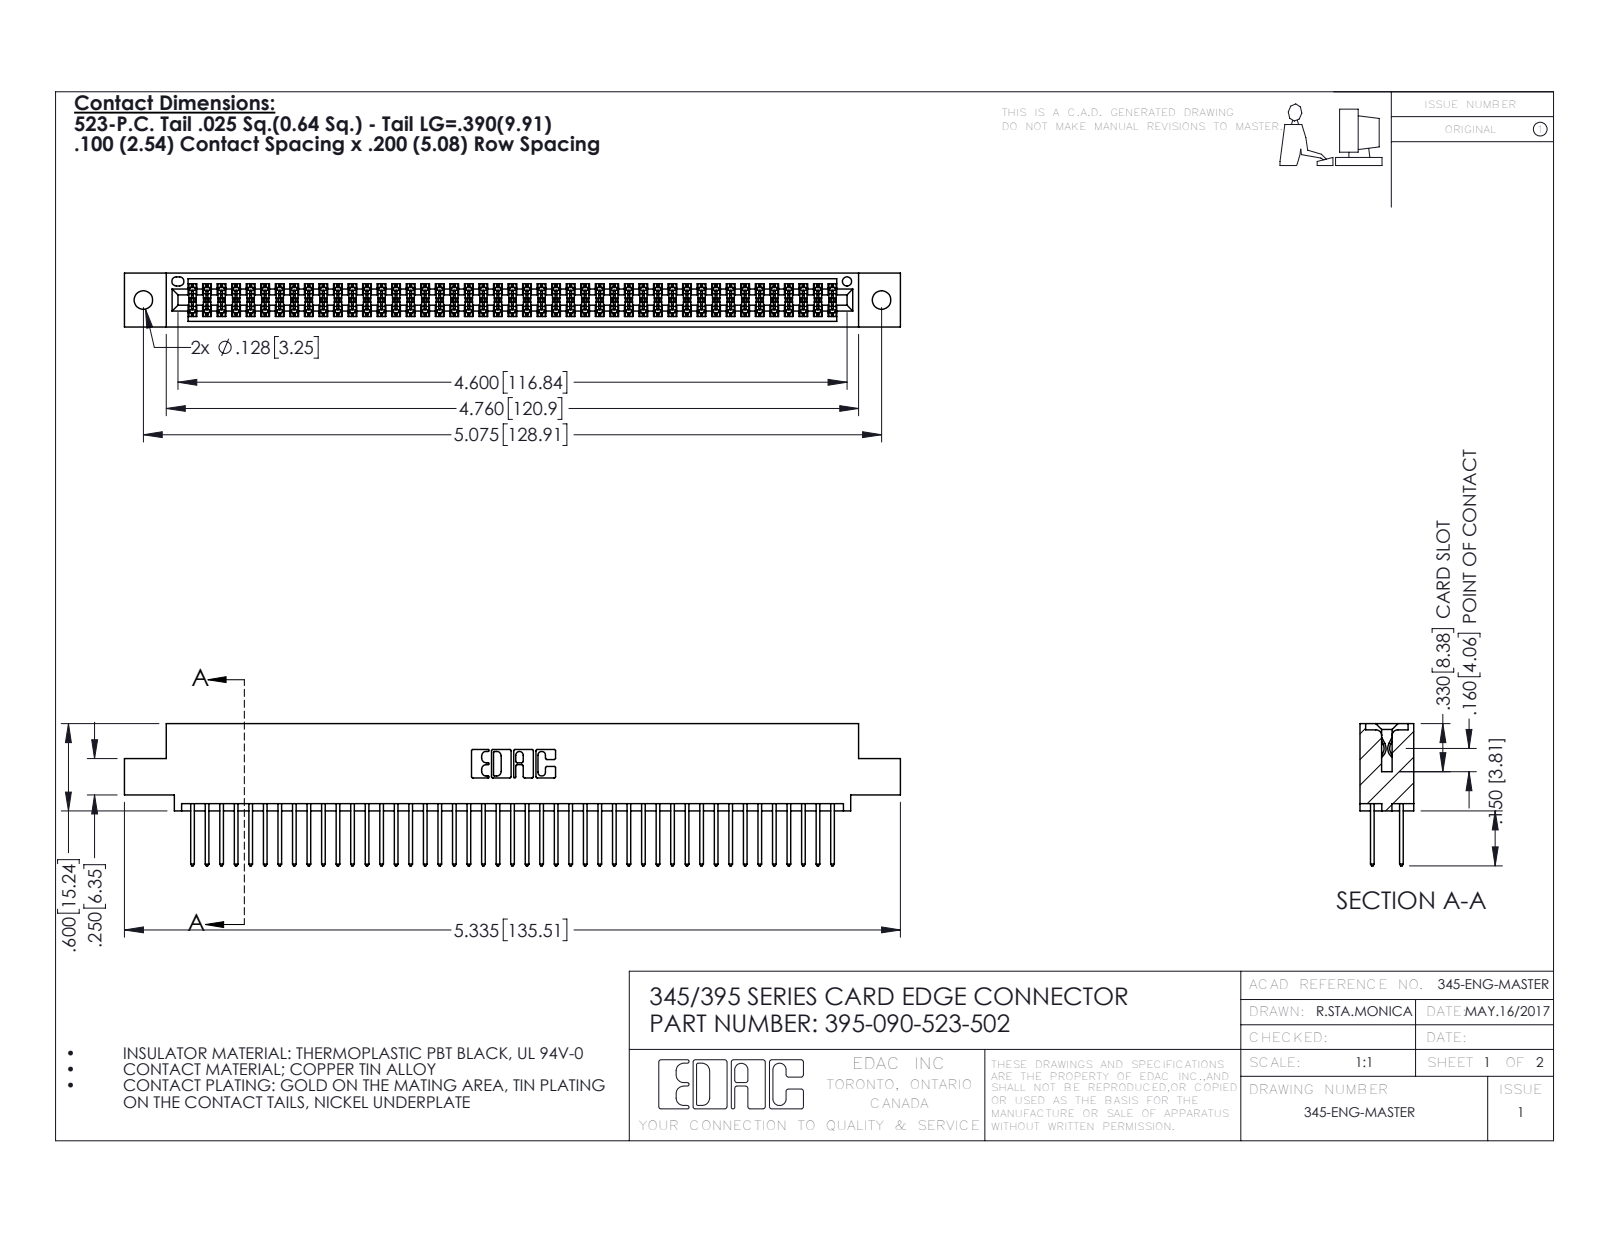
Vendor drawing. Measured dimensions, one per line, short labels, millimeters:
name: 345-292-001_345-293-123; 395-090-523-502; 345 Part_0.110 Offset - 0.128 Dia
written by: SolidWorks 2016 (CONFIG_CONTROL_DESIGN)
unit: mm
bodies: 91 solids, 4630 faces (3054 planar, 1576 cylindrical, 0 other)
size: 135.5 × 24.8 × 9.4
volume: 13 300 mm³; area: 20 320 mm²
holes: 2× ⌀3.3, 1× ⌀1.6
rounds: 135× R0.2, 90× R0.3, 22× R0.3, 6× R0.2, 6× R0.8, 3× R0.7, 2× R0.4, 2× R0.5
face distances: 7.6, 1.8, 5.1, 2.5, 6.9, 0.6, 9.4, 5.7, 4.4, 3.8
hole spacings: 6.9, 122.9, 128.9
